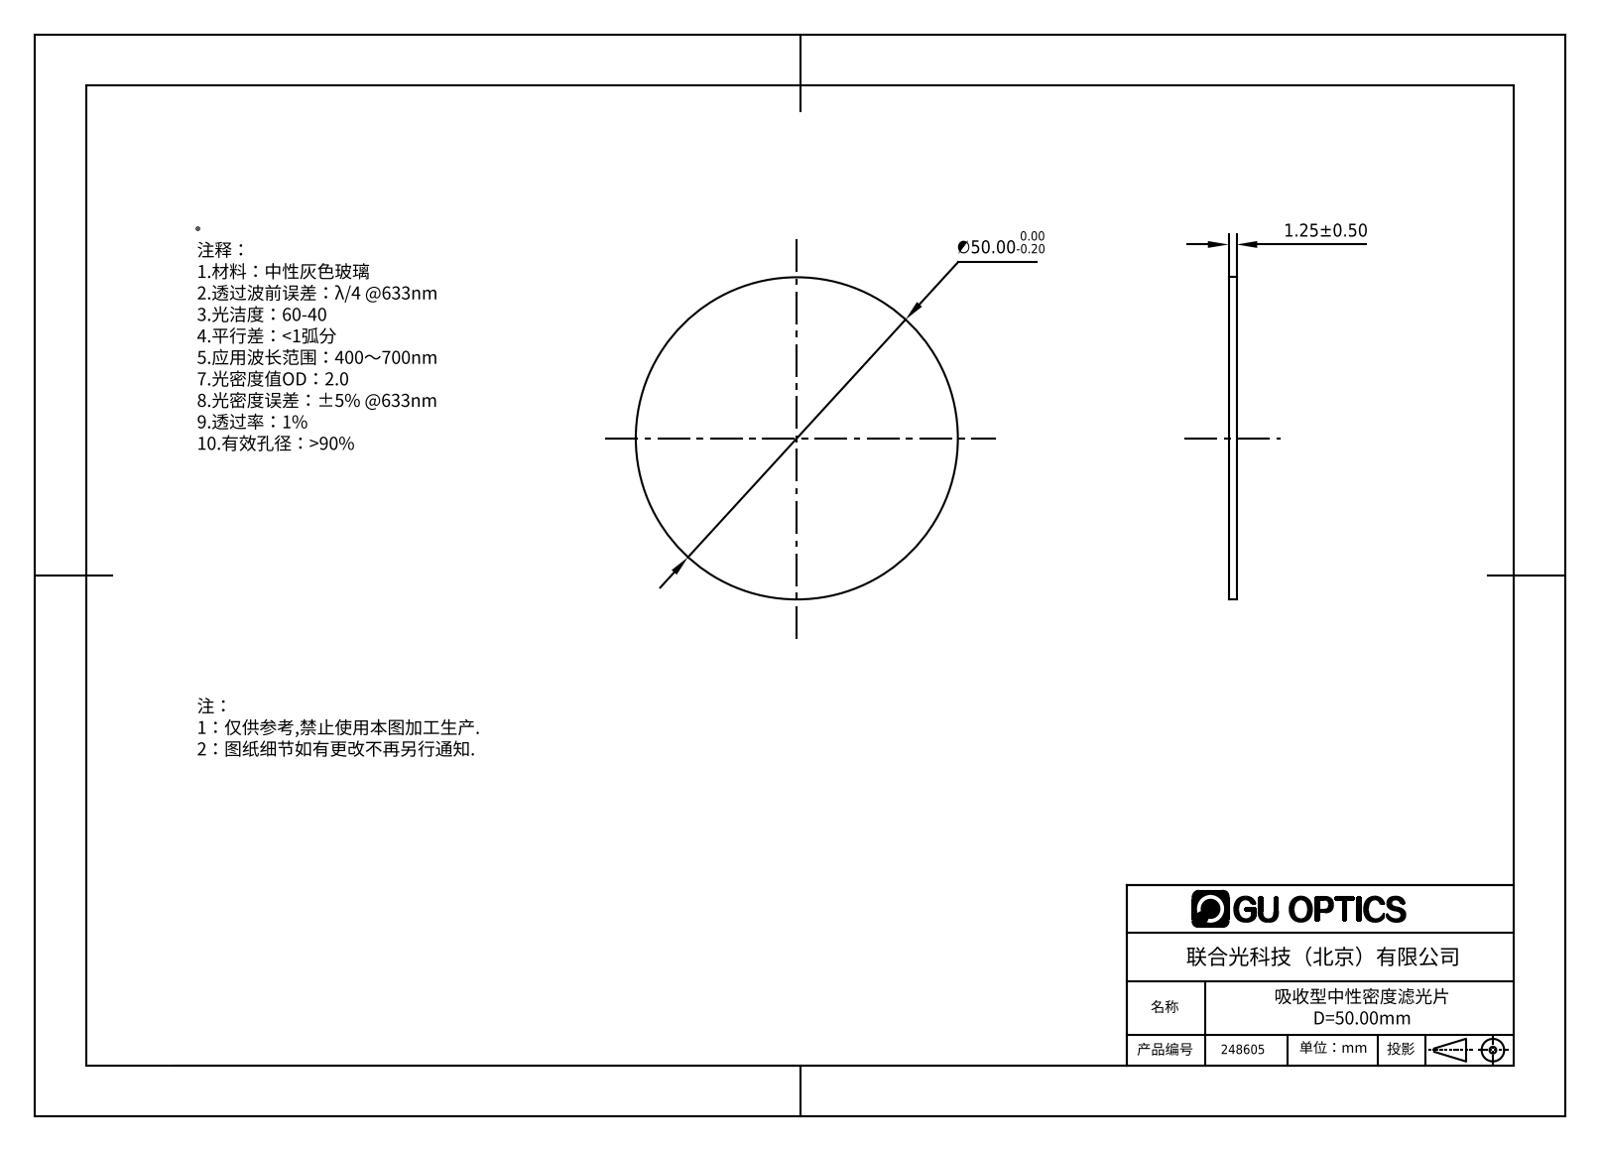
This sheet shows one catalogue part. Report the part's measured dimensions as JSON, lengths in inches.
{"part_name": "248605", "step_written_by": "SolidWorks 2016 (AUTOMOTIVE_DESIGN)", "units": "inches", "bodies": {"solids": 1, "faces": 4, "planar": 2, "cylindrical": 2, "other": 0}, "overall_size": [1.969, 1.969, 0.049], "volume_in3": 0.15, "surface_area_in2": 6.391, "round_bosses_or_shafts": [[1.969, 1]], "face_to_face_distances": [0.049]}
